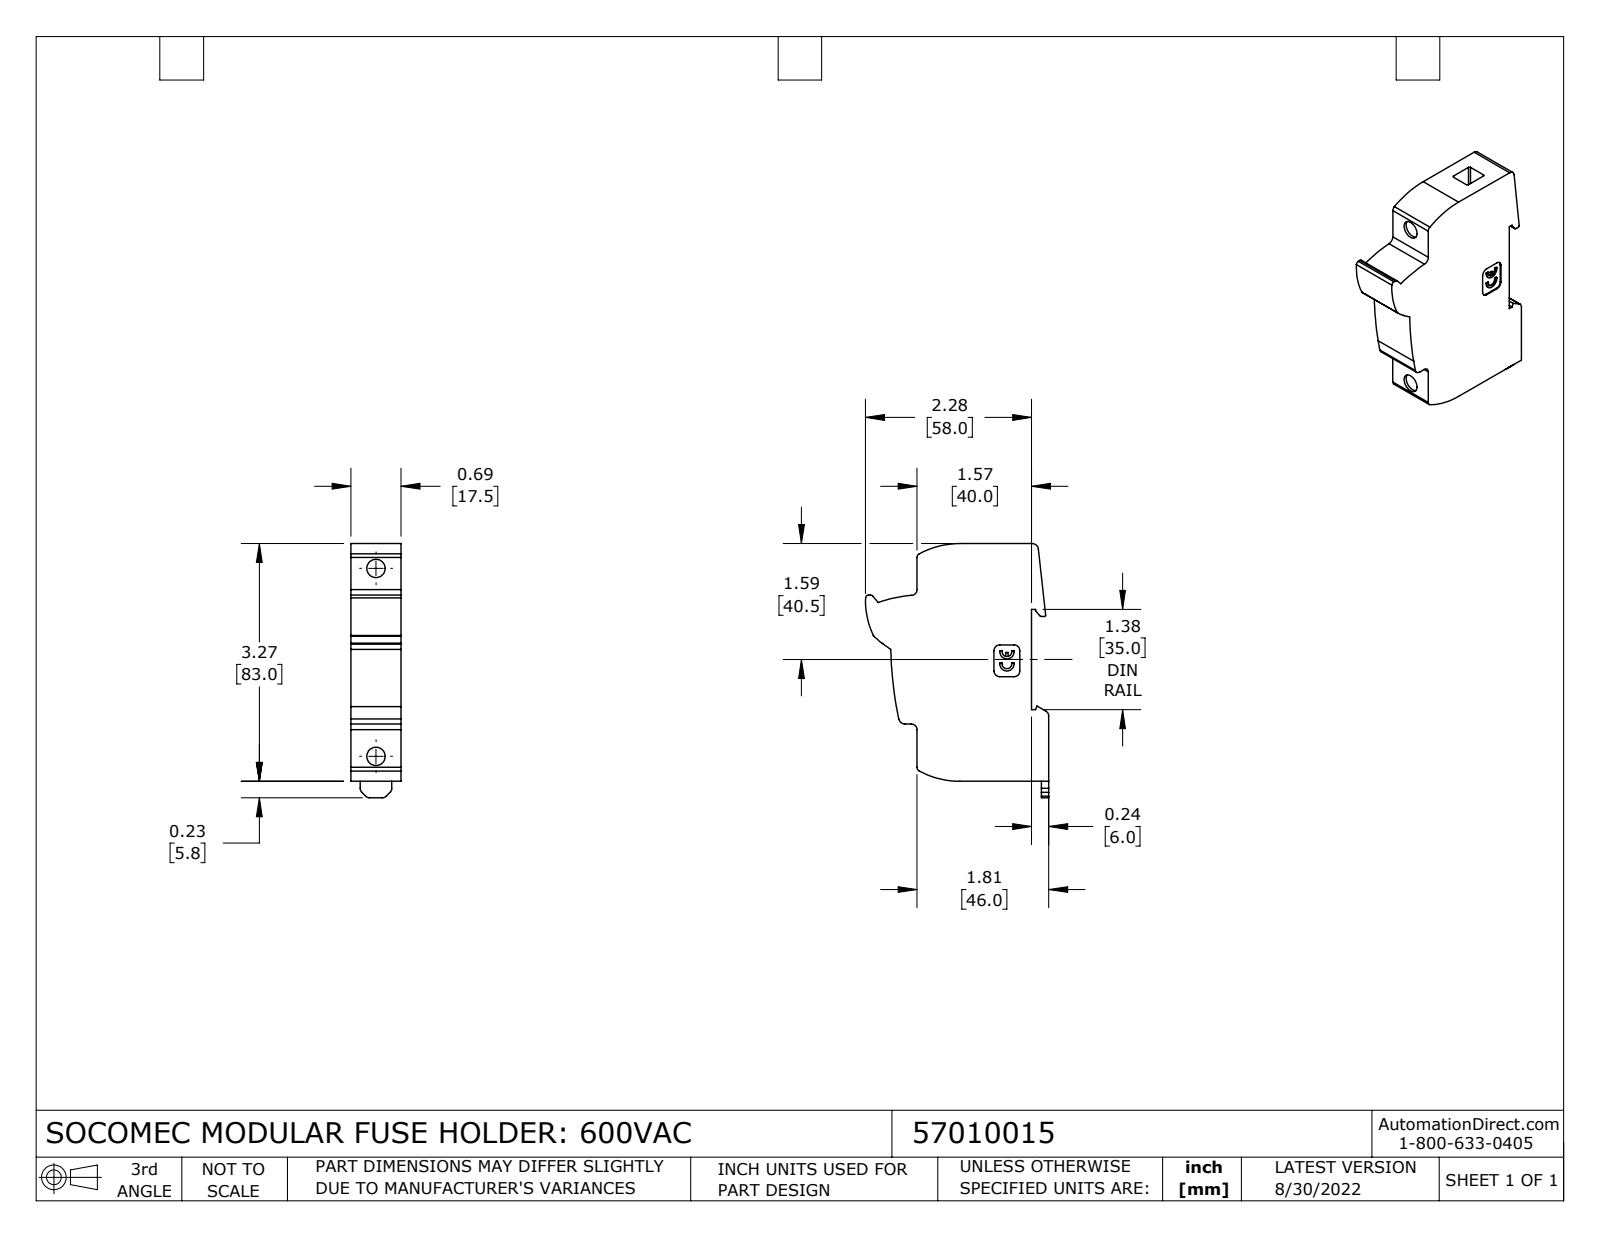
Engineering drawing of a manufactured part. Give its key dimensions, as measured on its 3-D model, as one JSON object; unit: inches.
{"part_name": "57010015", "step_written_by": "SolidWorks 2021 (CONFIG_CONTROL_DESIGN)", "units": "inches", "bodies": {"solids": 1, "faces": 105, "planar": 52, "cylindrical": 53, "other": 0}, "overall_size": [3.496, 2.52, 0.689], "volume_in3": 4.229, "surface_area_in2": 21.33, "round_holes": [[0.252, 2]], "partial_cylinders_radius": [[0.079, 11], [0.02, 5], [0.039, 4], [0.059, 2], [0.067, 2], [0.087, 2], [0.098, 2], [1.186, 2]], "face_to_face_distances": [0.689, 0.236, 1.575, 3.268, 1.811, 0.199, 0.49, 0.291, 0.518, 0.281], "hole_center_spacings": [2.583]}
